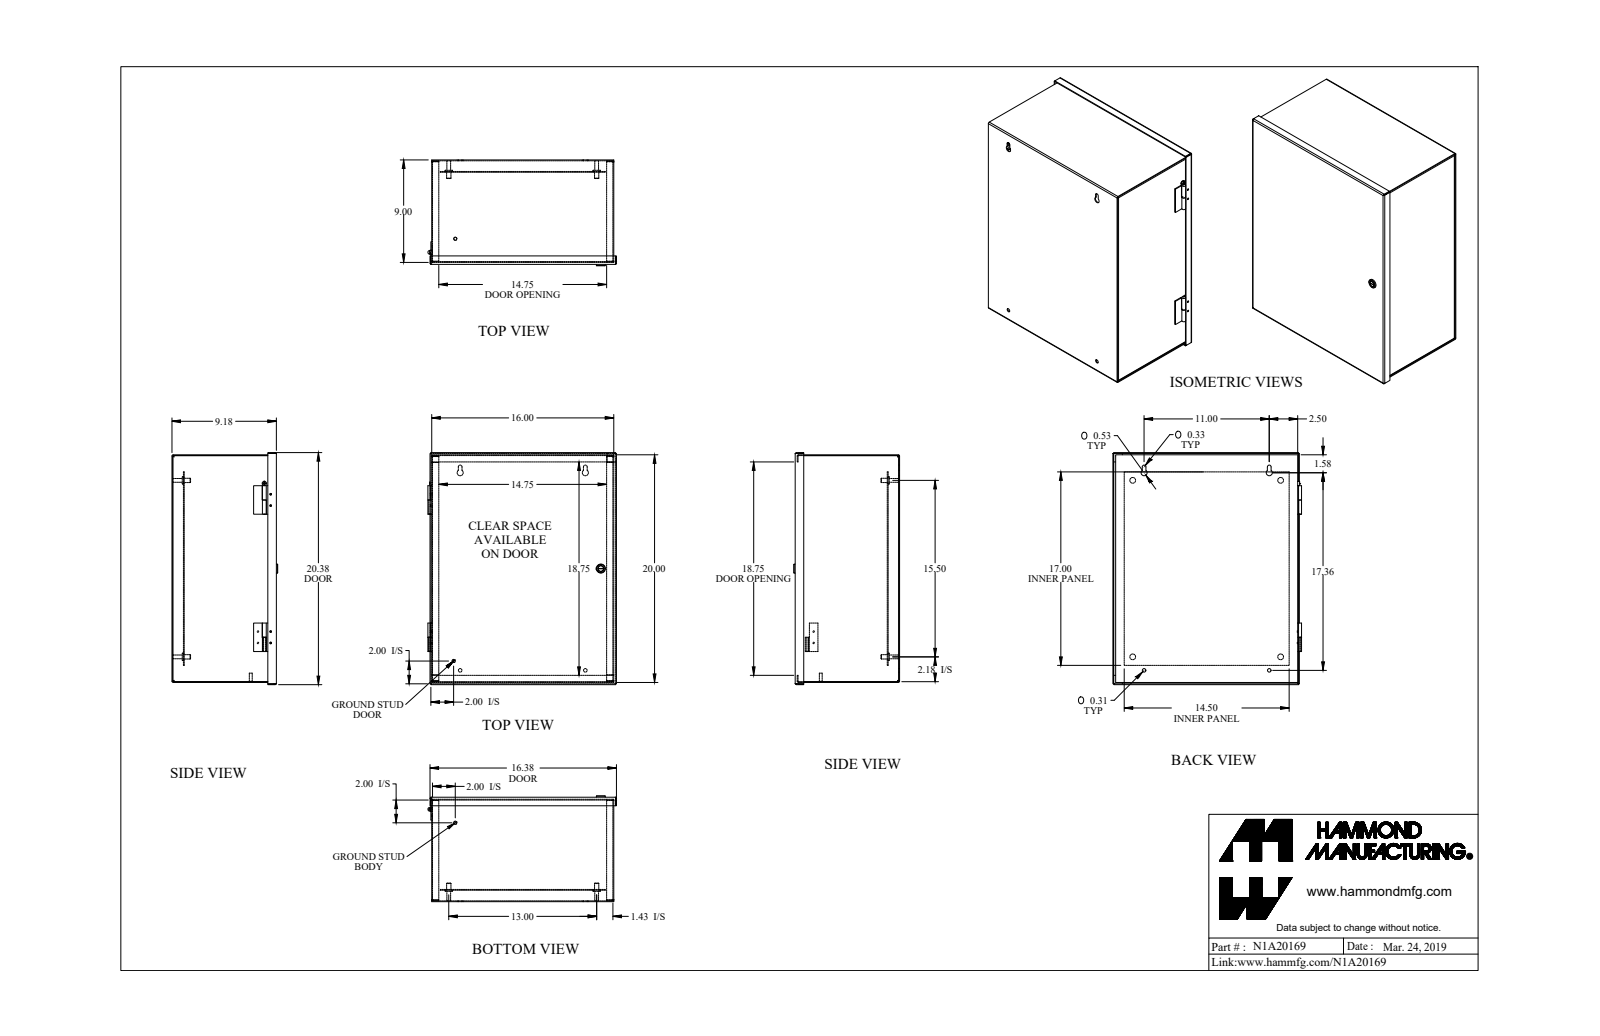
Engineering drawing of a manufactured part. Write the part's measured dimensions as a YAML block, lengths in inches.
part_name: "N1A20169"
step_written_by: "SolidWorks 2018 (AUTOMOTIVE_DESIGN)"
units: inches
bodies: {solids: 23, faces: 520, planar: 294, cylindrical: 182, other: 44}
overall_size: [20.384, 16.574, 9.299]
volume: 122
surface_area: 3399
round_holes:
  - {diameter: 0.14, count: 8}
  - {diameter: 0.5, count: 4}
  - {diameter: 0.307, count: 2}
  - {diameter: 0.312, count: 2}
  - {diameter: 0.445, count: 2}
  - {diameter: 0.17, count: 1}
  - {diameter: 0.187, count: 1}
  - {diameter: 0.516, count: 1}
round_bosses_or_shafts:
  - {diameter: 0.128, count: 8}
  - {diameter: 0.375, count: 5}
  - {diameter: 0.65, count: 4}
  - {diameter: 0.33, count: 4}
  - {diameter: 1, count: 2}
  - {diameter: 0.281, count: 2}
  - {diameter: 0.25, count: 2}
  - {diameter: 0.788, count: 1}
partial_cylinders:
  - {radius: 0.036, count: 16}
  - {radius: 0.108, count: 16}
  - {radius: 0.06, count: 2}
  - {radius: 0.153, count: 2}
  - {radius: 0.164, count: 2}
  - {radius: 0.266, count: 2}
  - {radius: 0.03, count: 1}
  - {radius: 0.125, count: 1}
face_to_face_distances: [0.072, 9.105, 1.009, 8.096, 15.928, 9.033, 9.177, 19.928, 1.081, 8.024]
hole_center_spacings: [1, 1.119, 1.553, 2.031, 7.758, 12.059, 12.062, 12.062]
